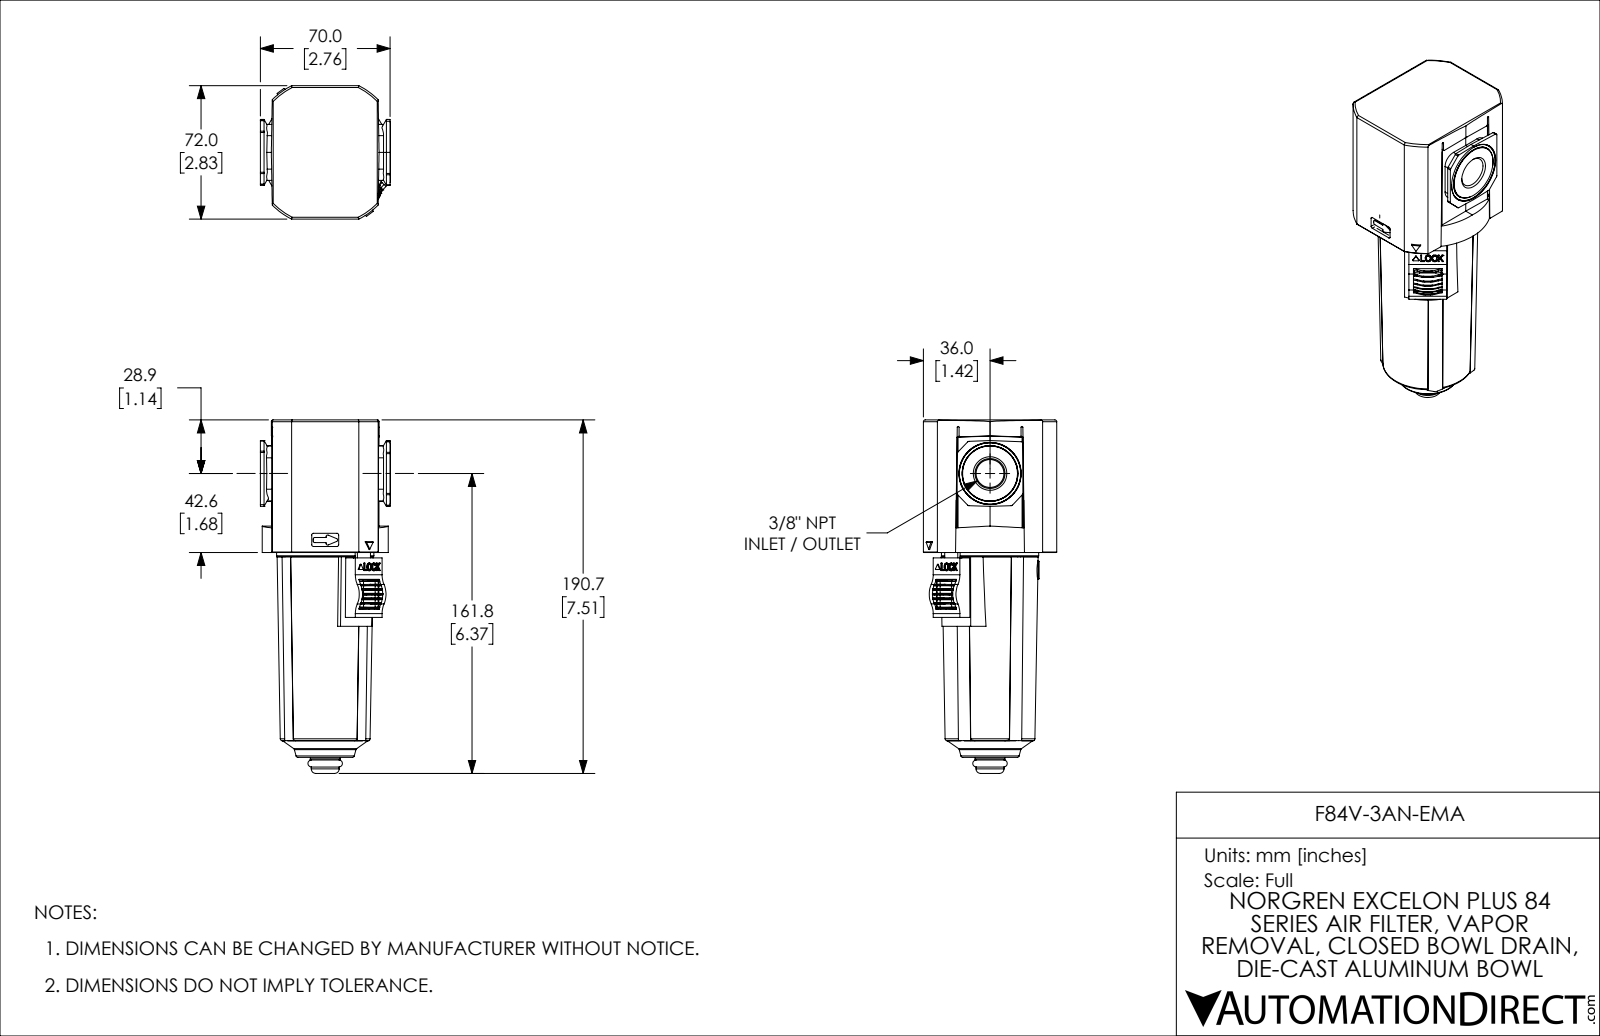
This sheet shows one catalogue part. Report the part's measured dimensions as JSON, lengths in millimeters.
{"part_name": "F84V-3AN-EMA", "step_written_by": "SolidWorks 2021 (CONFIG_CONTROL_DESIGN)", "units": "millimeters", "bodies": {"solids": 5, "faces": 998, "planar": 416, "cylindrical": 364, "other": 218}, "overall_size": [190.7, 72, 70.3], "volume_mm3": 444900, "surface_area_mm2": 95030, "round_holes": [[4.1, 2], [3.2, 1], [6.8, 1], [16.1, 1], [62.5, 1]], "round_bosses_or_shafts": [[8, 2], [7, 2], [53.9, 1], [52.5, 1], [51.3, 1], [49.8, 1], [49.6, 1], [23, 1]], "partial_cylinders_radius": [[1, 46], [0.5, 37], [0.7, 16], [0.3, 14], [0.2, 8], [1, 8], [1.1, 8], [1.5, 8]], "face_to_face_distances": [1.5, 61.2, 59.7, 72, 52, 70, 50.5, 9.2, 10.3, 19.5], "hole_center_spacings": [15.1, 30.2]}
